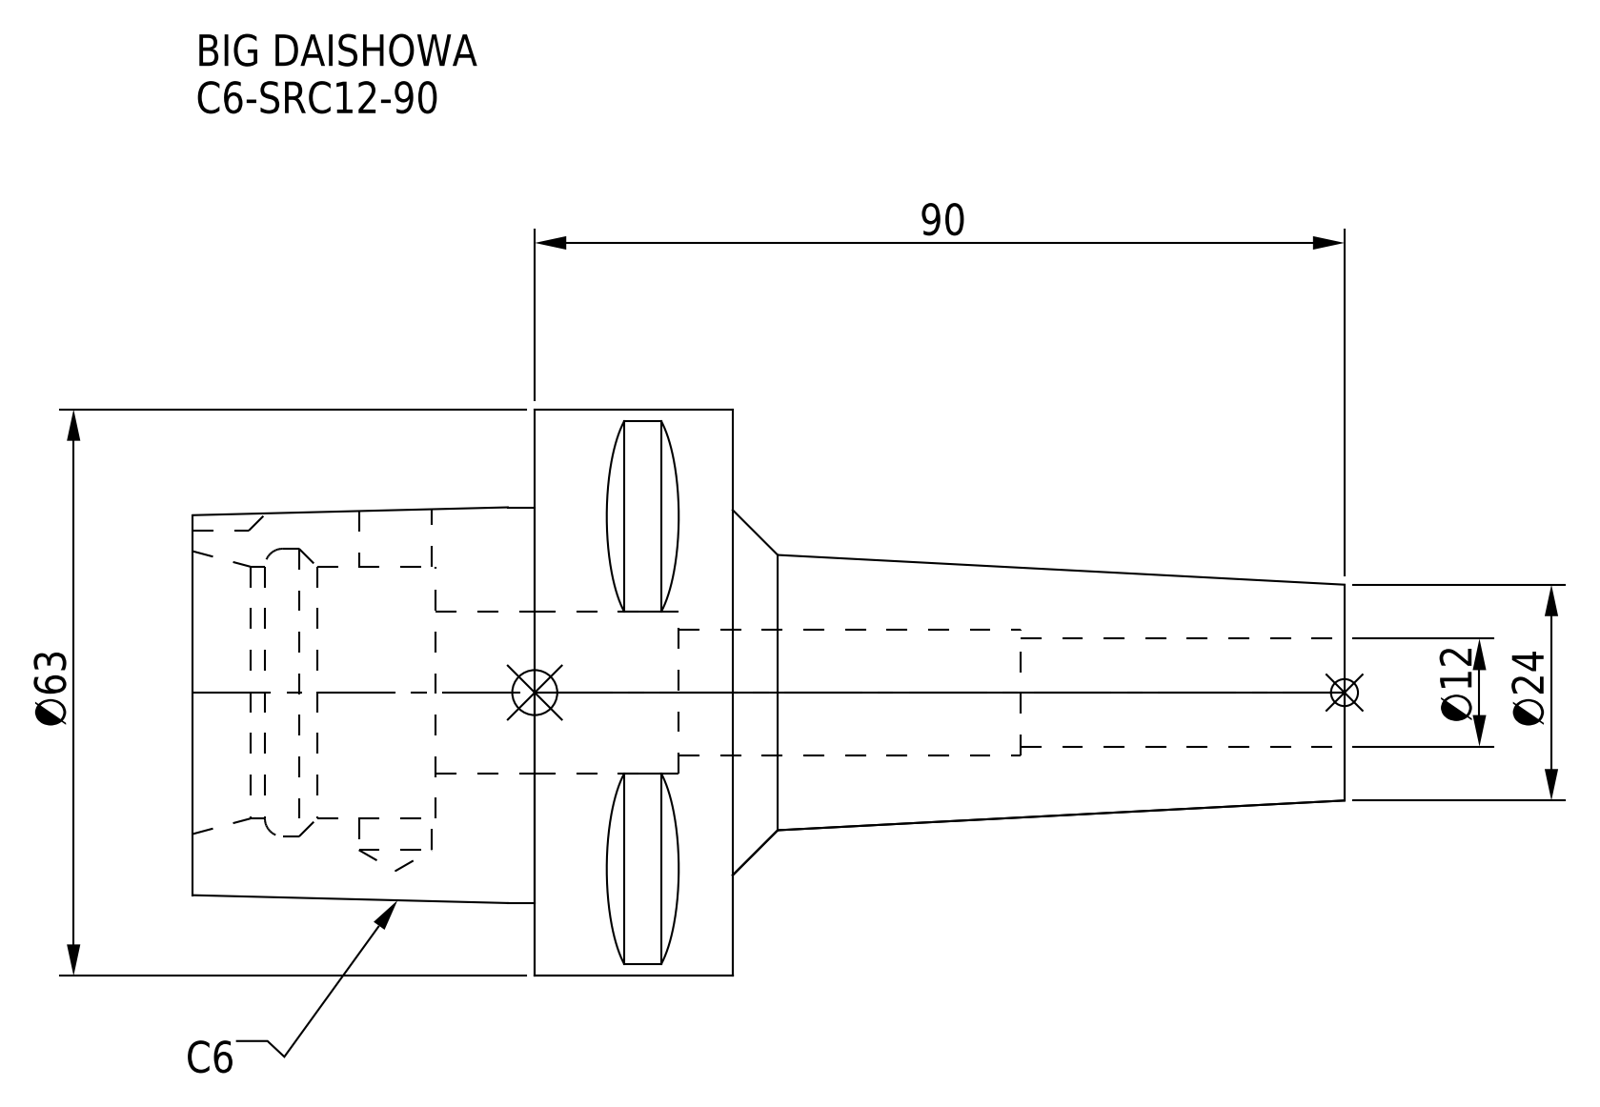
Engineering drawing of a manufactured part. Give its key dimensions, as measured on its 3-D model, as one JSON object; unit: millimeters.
{"part_name": "C6-SRC12-90", "step_written_by": "CREO PARAMETRIC BY PTC INC, 2016380 (AUTOMOTIVE_DESIGN)", "units": "millimeters", "bodies": {"solids": 1, "faces": 62, "planar": 29, "cylindrical": 19, "other": 14}, "overall_size": [128, 63, 63], "volume_mm3": 128736, "surface_area_mm2": 28311, "round_holes": [[8.1, 1], [12, 1], [14, 1], [18, 1], [28, 1], [32, 1]], "round_bosses_or_shafts": [[63, 1]], "partial_cylinders_radius": [[5, 1]], "face_to_face_distances": [22, 38, 60, 27, 33, 11, 68, 90, 101, 128]}
